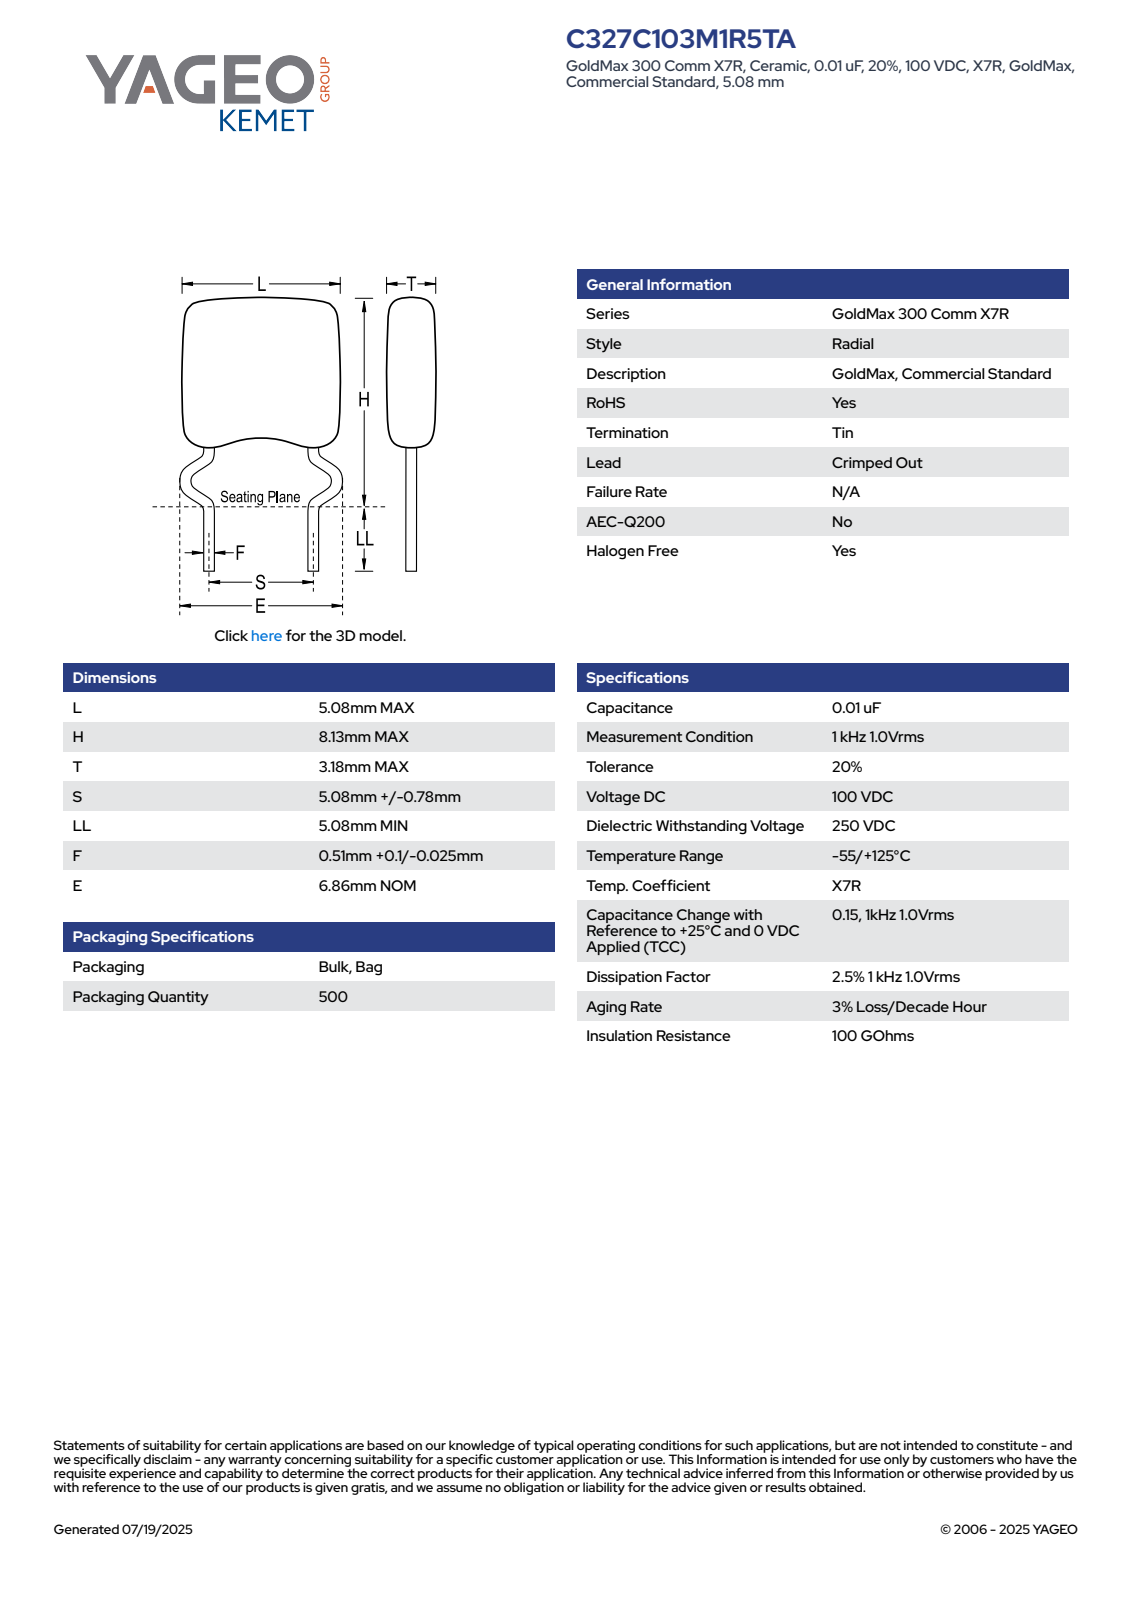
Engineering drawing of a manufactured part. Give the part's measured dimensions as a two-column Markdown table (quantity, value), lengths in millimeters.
| quantity | value |
| --- | --- |
| part name | CCR_RCCR_C327_L5.08H8.13T3.18S5.08LL5.08F0.51E6.86 |
| STEP written by | SolidWorks 2014 (AUTOMOTIVE_DESIGN) |
| units | millimeters |
| bodies | 4 solids, 104 faces (66 planar, 16 cylindrical, 22 other) |
| overall size | 13.21 × 6.86 × 3.19 |
| volume | 82 mm³ |
| surface area | 138 mm² |
| round bosses / shafts (diameter × count) | 0.51 × 2 |
| partial cylindrical surfaces (radius × count) | 0.26 × 8, 0.75 × 4 |
| main face-to-face distances | 3.18, 5.08, 5.12, 3.19, 8.09, 13.21, 2.23, 2.89, 0.81, 10.98 |
